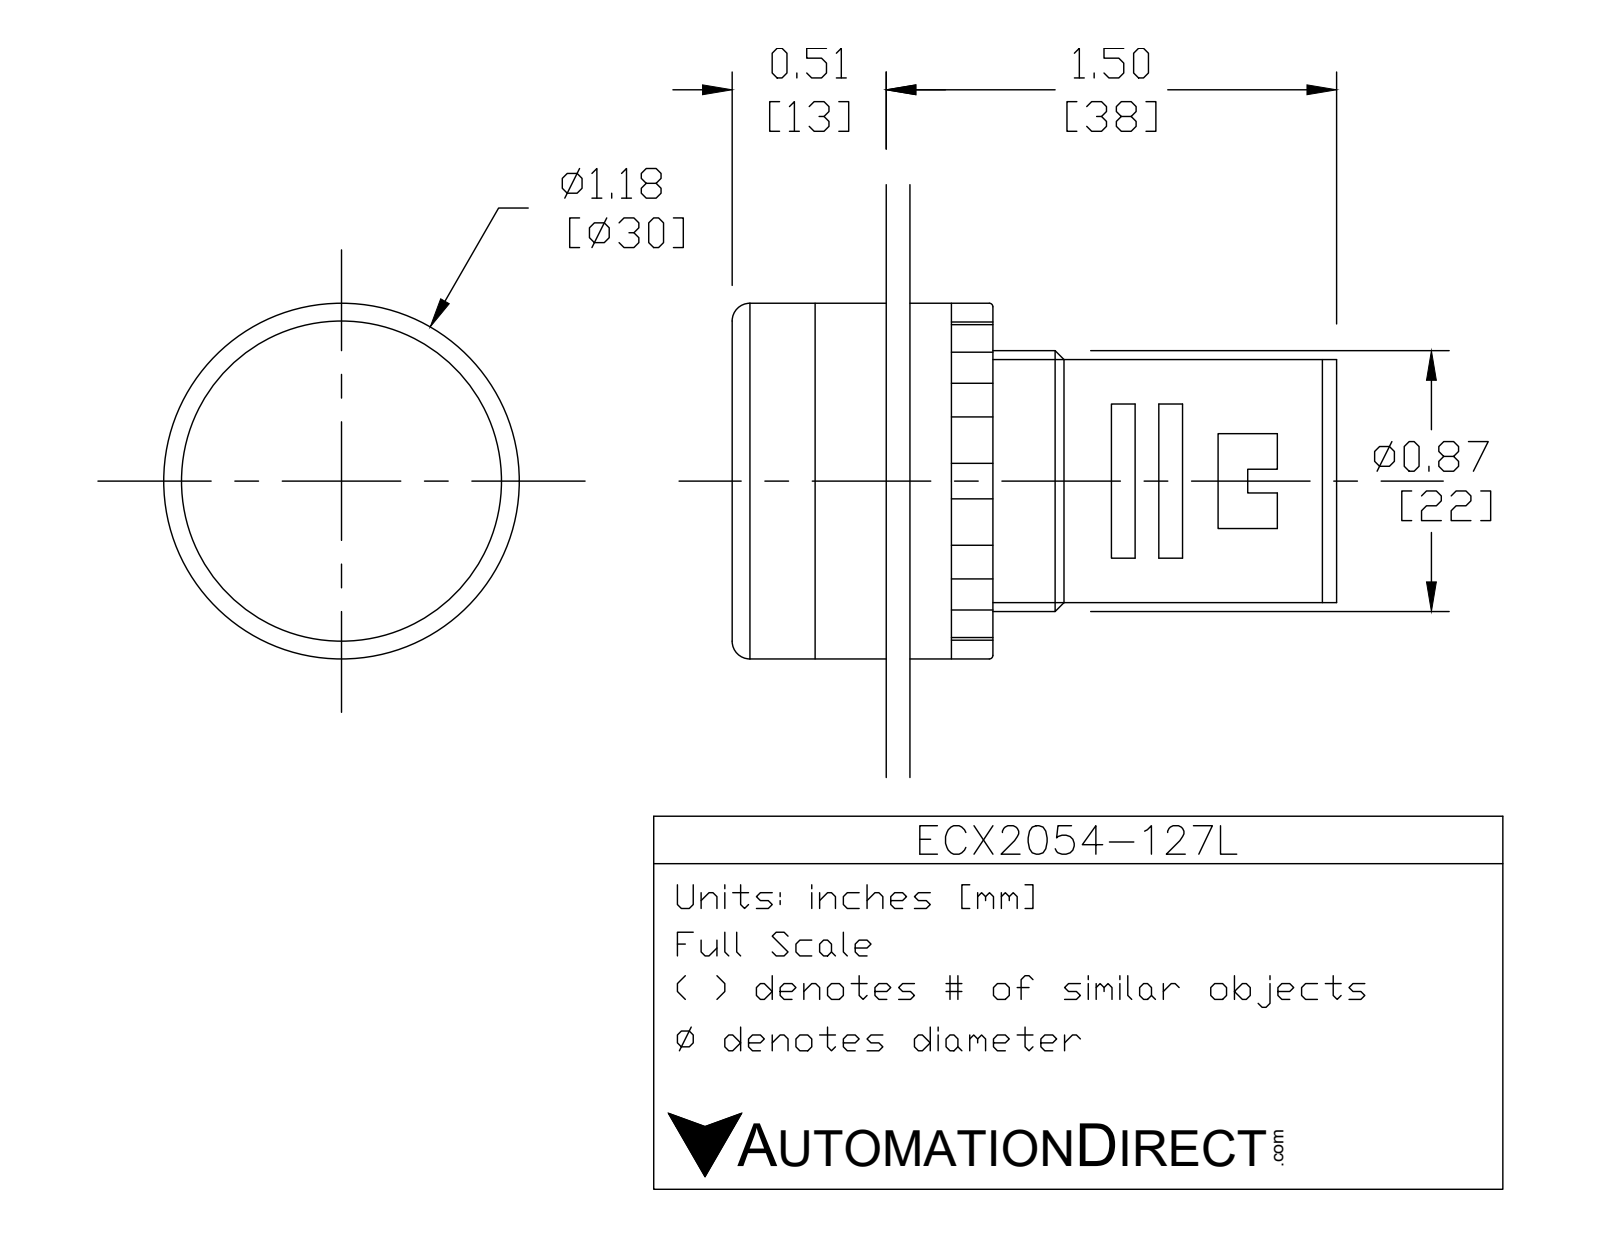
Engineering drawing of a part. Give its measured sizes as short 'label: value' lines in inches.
name: ECX2054-127L
written by: SolidWorks 2017 (AUTOMOTIVE_DESIGN)
unit: in
bodies: 6 solids, 123 faces (63 planar, 39 cylindrical, 21 other)
size: 2.008 × 1.181 × 1.181
volume: 1.372 in³; area: 15.24 in²
holes: 2× ⌀0.217, 1× ⌀0.886
bosses: 2× ⌀0.157, 1× ⌀1.181, 1× ⌀1.142, 1× ⌀1.043, 1× ⌀0.866, 1× ⌀0.787
rounds: 12× R0.039
face distances: 0.236, 0.748, 0.512, 0.276, 0.079, 0.984, 0.157, 0.472, 0.669, 0.591
hole spacings: 0.182, 0.364
